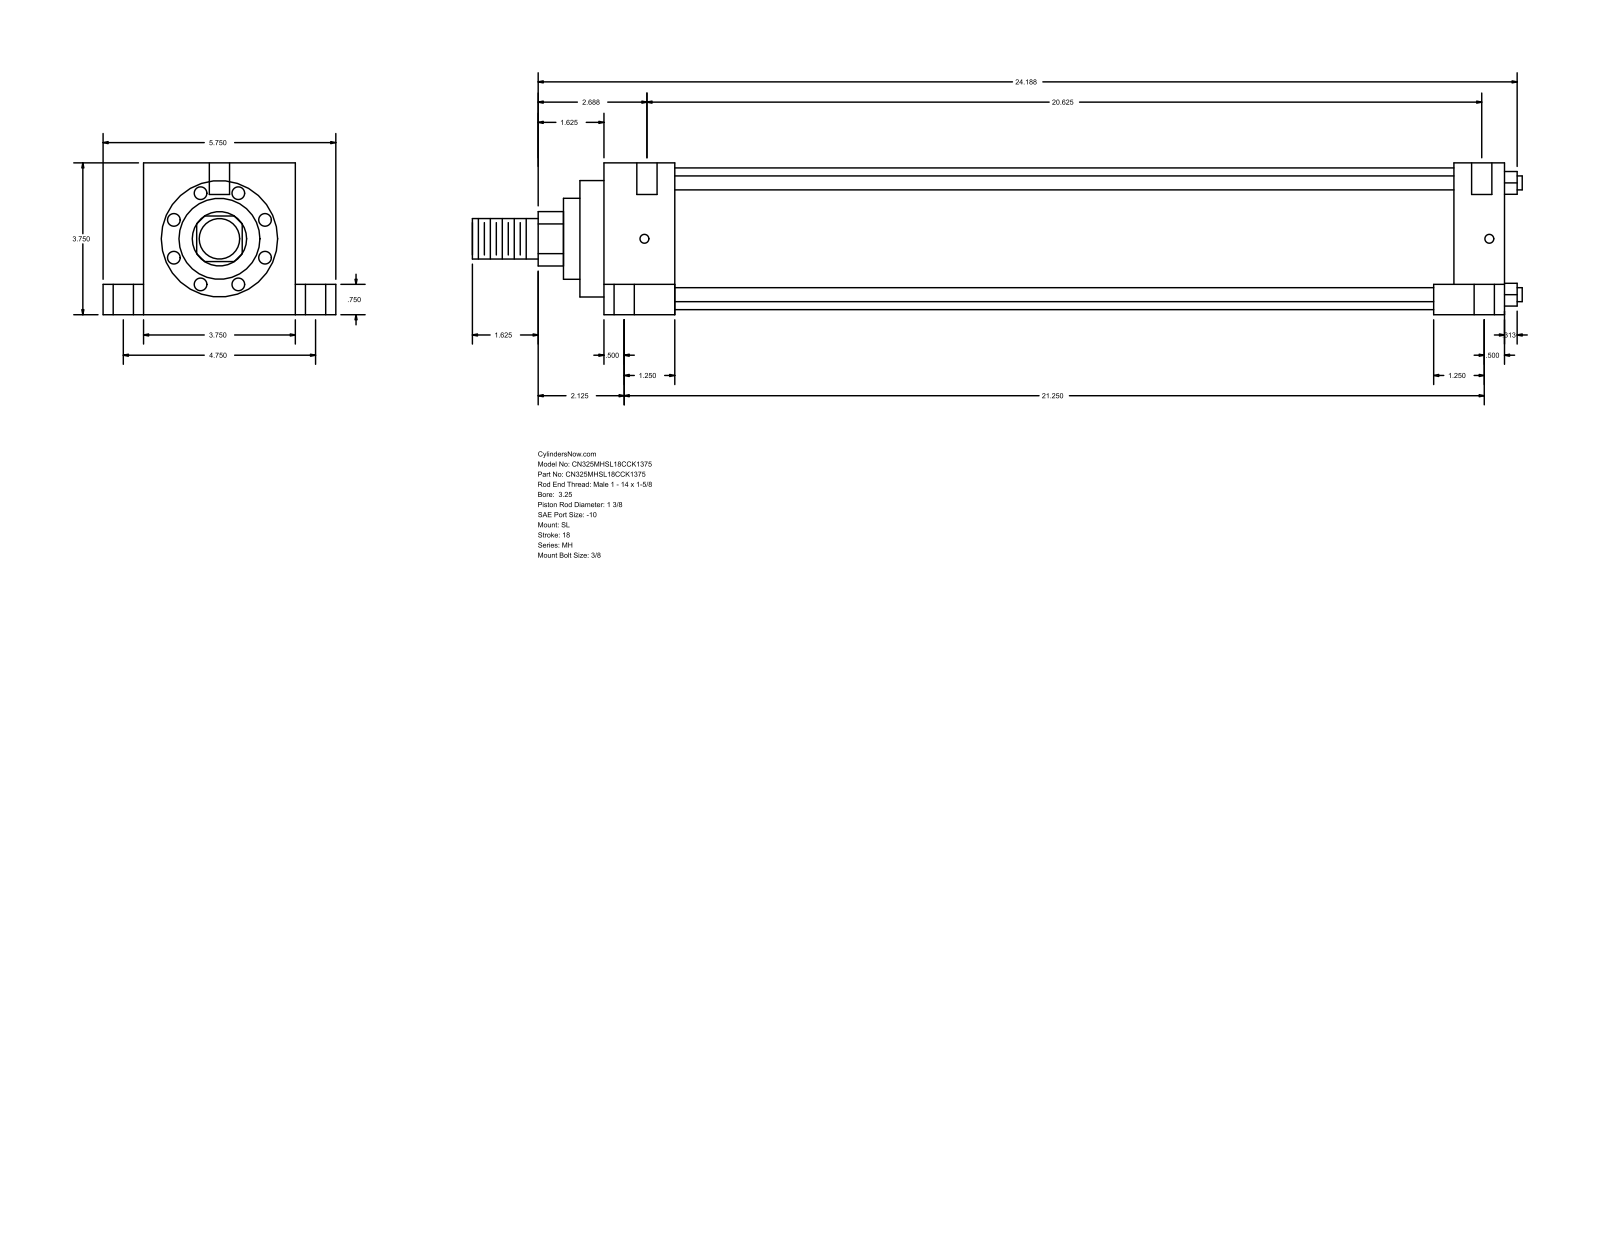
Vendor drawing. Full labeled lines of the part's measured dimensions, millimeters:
Part name (STEP PRODUCT): MH_SL__0325_1.375
STEP written by: GSSL Pune (CONFIG_CONTROL_DESIGN)
Units: millimetres
Bodies: 0 solids, 110 faces (77 planar, 33 cylindrical, 0 other)
Overall size (bounding box): 658.81 × 146.05 × 95.25
Round holes (diameter × count): ⌀12.7 ×6, ⌀5.56 ×4, ⌀19.05 ×4
Round bosses / shafts (diameter × count): ⌀8.76 ×4, ⌀88.9 ×1, ⌀73.03 ×1, ⌀50.8 ×1, ⌀34.92 ×1, ⌀25.4 ×1
Partial cylindrical surfaces — rounded edges, fillets, slot ends (radius × count): R17.06 ×1
Main face-to-face distances: 95.24, 565.15, 44.45, 520.7, 25.41, 120.65, 19.05, 76.19, 533.4, 488.95
Hole centre spacings: 60.35, 60.41, 61.65, 62, 120.66, 528.92, 530.23, 530.5
